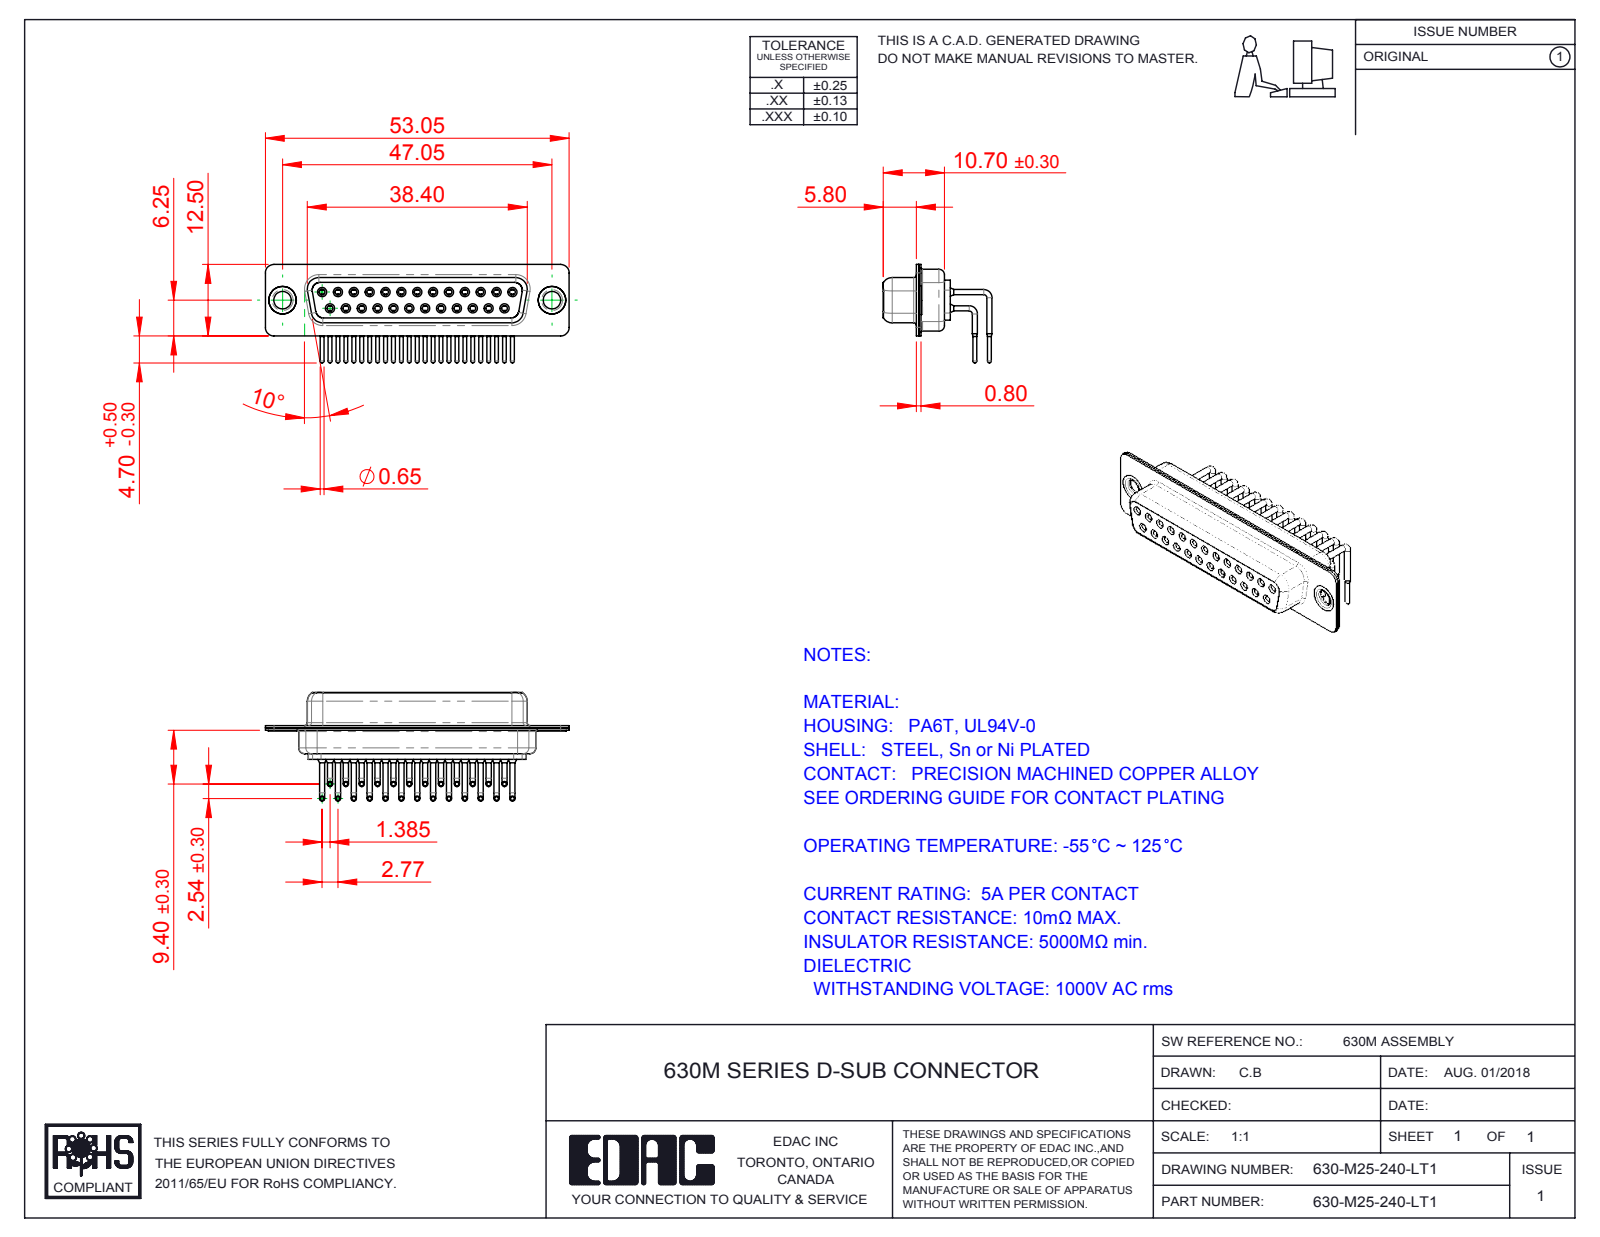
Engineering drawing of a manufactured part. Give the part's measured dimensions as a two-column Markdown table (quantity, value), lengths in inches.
| quantity | value |
| --- | --- |
| part name | 630-M25-240-LT1; 630M Shell Front_25 Contacts; 630M Thru Hole Rivet; 630M Shell Rear_25 Contacts (+3 more) |
| STEP written by | SolidWorks 2016 (CONFIG_CONTROL_DESIGN) |
| units | inches |
| bodies | 30 solids, 1578 faces (442 planar, 696 cylindrical, 440 other) |
| overall size | 2.089 × 0.748 × 0.677 |
| volume | 0.233 in³ |
| surface area | 14.85 in² |
| round holes (diameter × count) | 0.039 × 25, 0.043 × 25, 0.067 × 25, 0.071 × 25, 0.079 × 25, 0.12 × 2, 0.157 × 2, 0.189 × 2 |
| round bosses / shafts (diameter × count) | 0.035 × 50, 0.063 × 25, 0.059 × 25, 0.026 × 25, 0.197 × 2, 0.193 × 2, 0.14 × 2 |
| partial cylindrical surfaces (radius × count) | 0.059 × 16, 0.079 × 12, 0.053 × 10, 0.063 × 8, 0.01 × 4, 0.02 × 4, 0.024 × 4, 0.026 × 4 |
| main face-to-face distances | 0.016, 0.057, 0.352, 0.244, 0.075, 0.335, 0.278, 0.018, 0.091, 0.033 |
| hole center spacings | 0.124, 0.109, 0.218, 0.327, 0.436, 0.545, 0.198, 0.295 |
